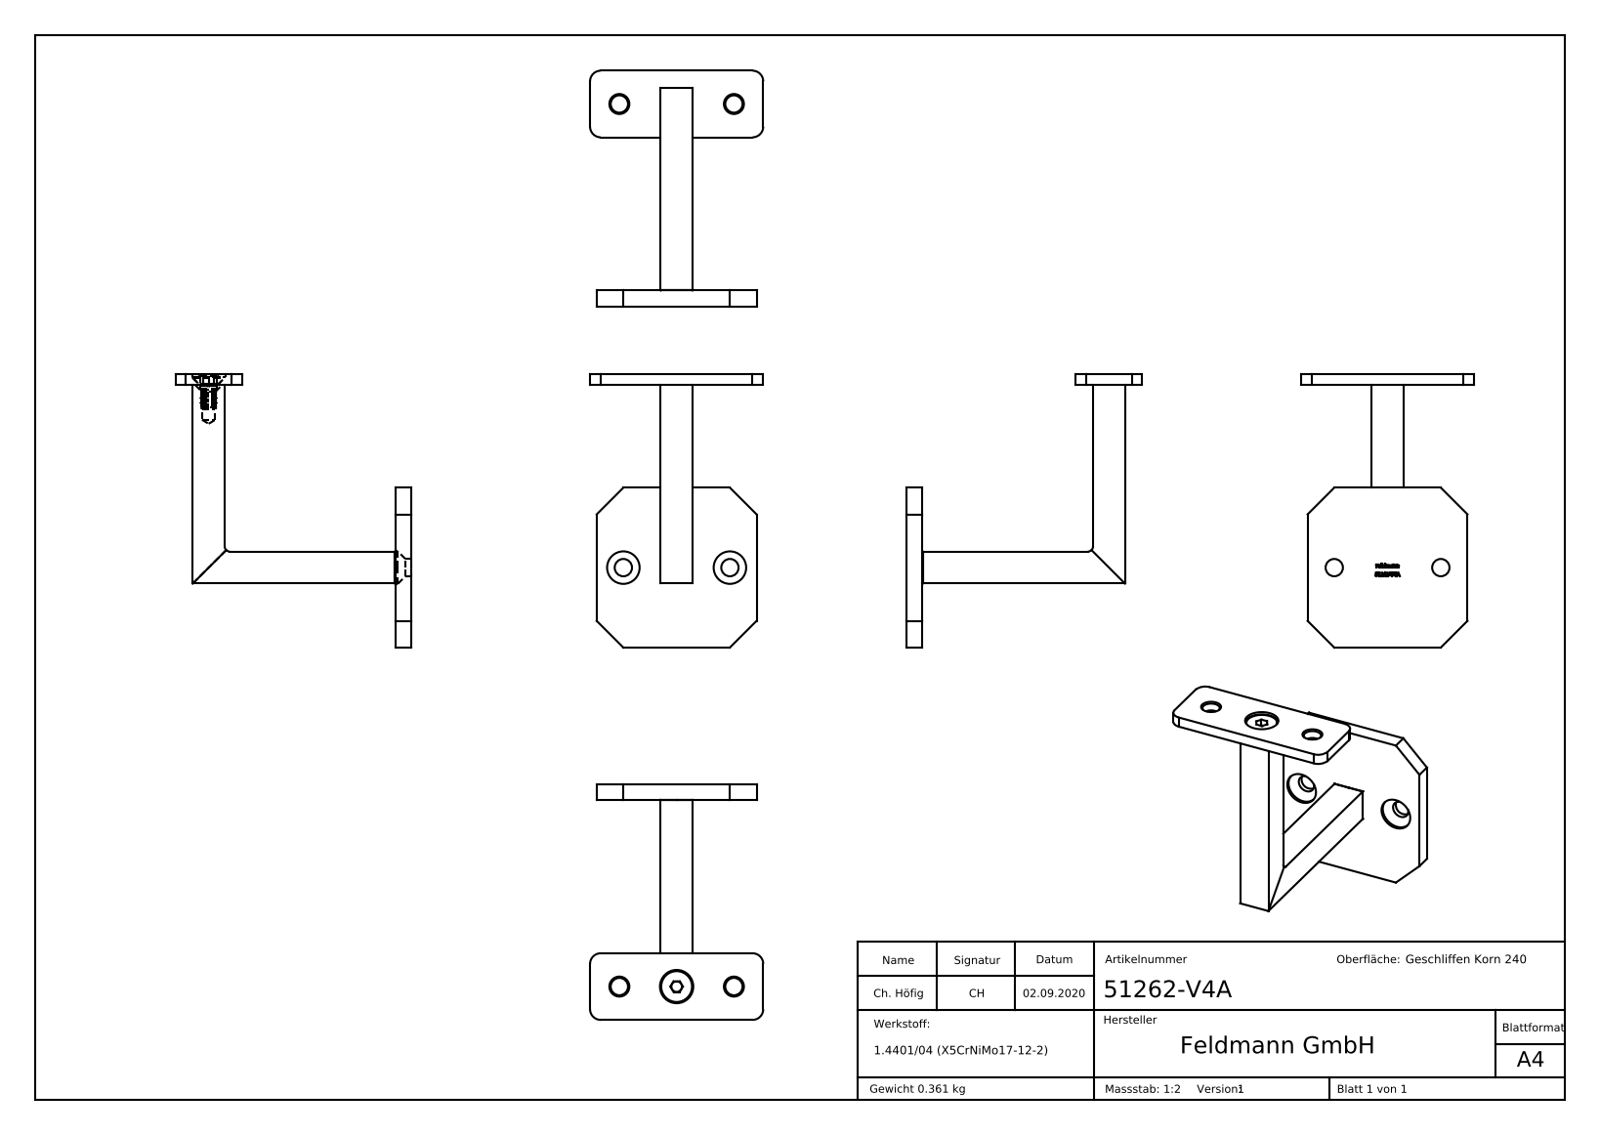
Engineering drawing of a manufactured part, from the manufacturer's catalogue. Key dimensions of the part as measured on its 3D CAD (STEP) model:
Part name (STEP PRODUCT): 5126X-XXX Teil3; 5126X-XXX Teil1_51262-V4A Teil1; 5126X-XXX Teil3_51263-V4A Teil3; 5126X-XXX Teil2 (+7 more)
STEP written by: SolidWorks 2018 (CONFIG_CONTROL_DESIGN)
Units: millimetres
Bodies: 5 solids, 432 faces (201 planar, 74 cylindrical, 157 other)
Overall size (bounding box): 102.5 × 88.5 × 65
Volume: 47 875 mm³ · Surface area: 21 456 mm²
Round holes (diameter × count): ⌀6.5 ×4, ⌀12.2 ×2, ⌀5 ×1, ⌀5.5 ×1, ⌀7 ×1, ⌀10 ×1, ⌀12.5 ×1
Round bosses / shafts (diameter × count): ⌀11.57 ×1, ⌀6 ×1, ⌀4.02 ×1
Partial cylindrical surfaces — rounded edges, fillets, slot ends (radius × count): R4 ×4, R2 ×1, R6 ×1
Main face-to-face distances: 12, 6, 4, 76, 82, 78.5, 70, 24, 36, 74.5
Hole centre spacings: 21.5, 52, 40, 43
